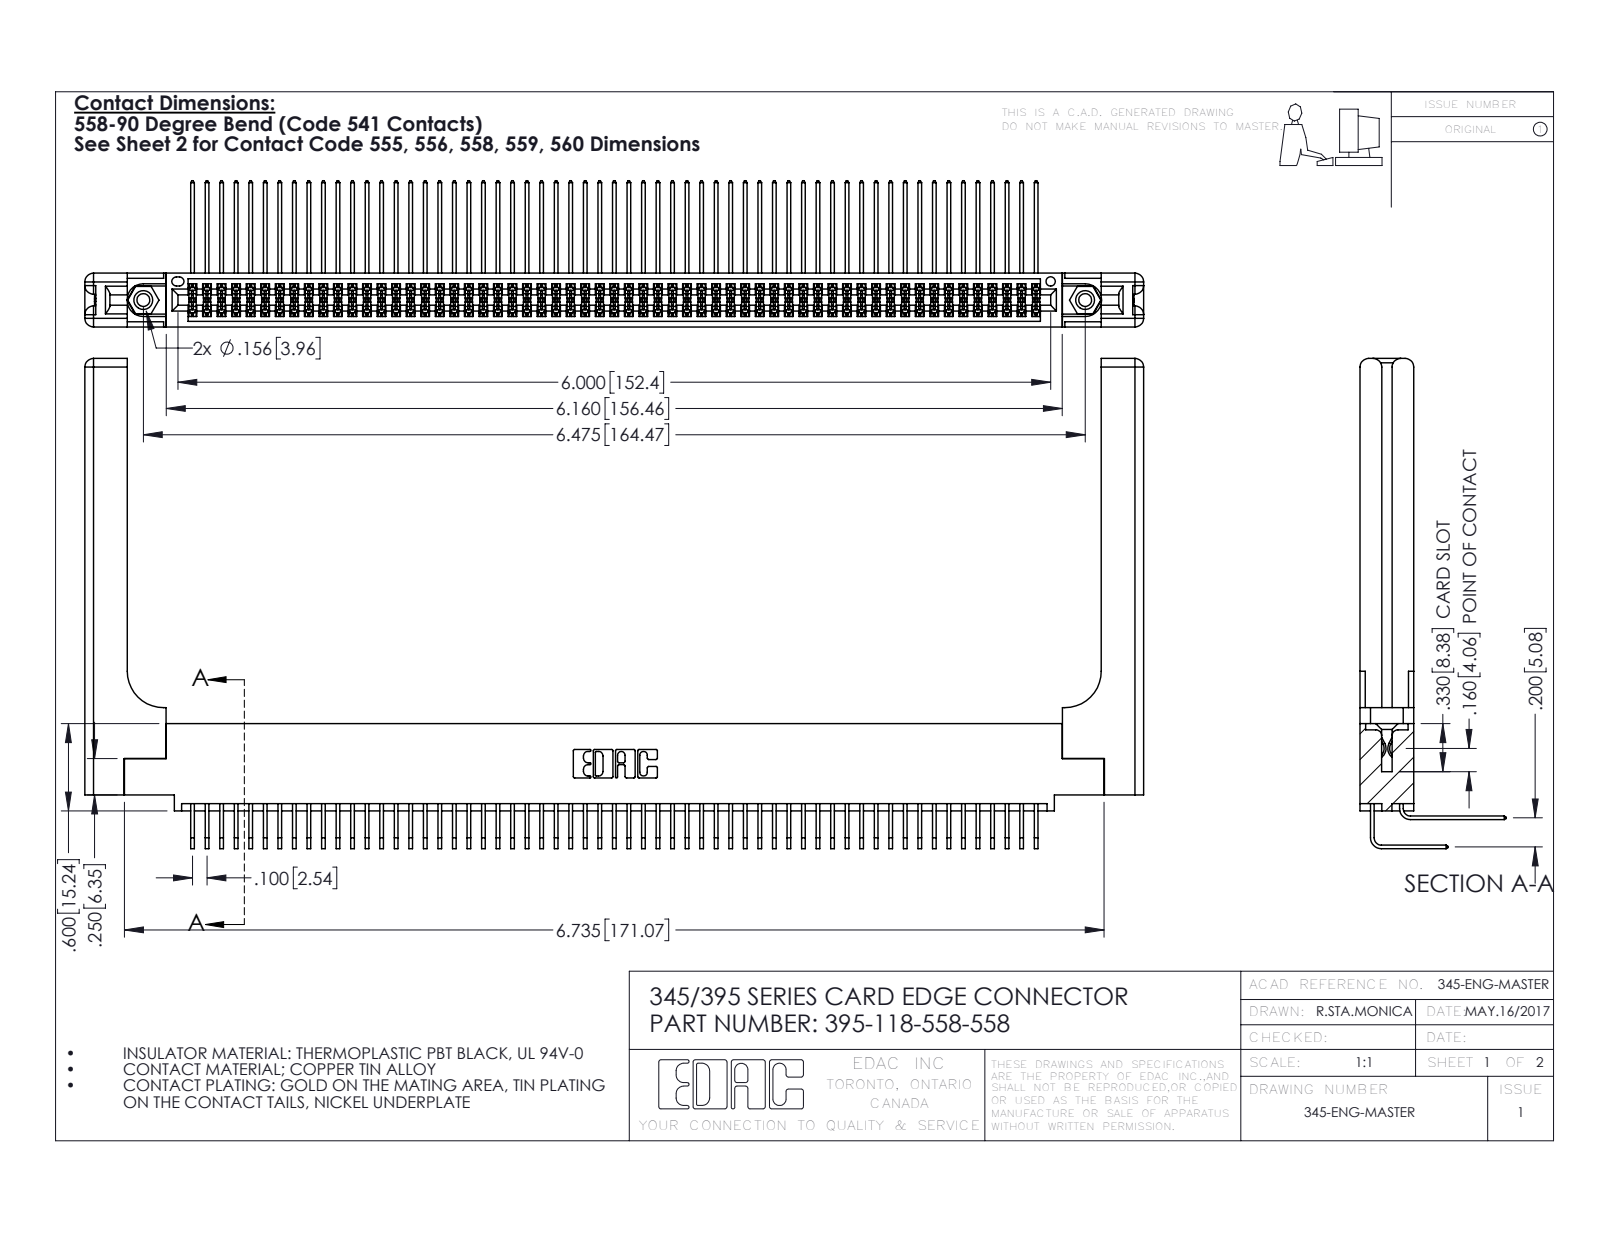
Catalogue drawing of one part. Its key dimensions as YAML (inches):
part_name: "345-220-058_345-220-058; 345 Part_0.110 Offset - 0.156 Dia-TH; 395-118-558-558; 345-292-001_558 559 Tail - 1 (+2 more)"
step_written_by: "SolidWorks 2016 (CONFIG_CONTROL_DESIGN)"
units: inches
bodies: {solids: 123, faces: 6522, planar: 4362, cylindrical: 2100, other: 60}
overall_size: [7.279, 3.369, 1.005]
volume: 1.66
surface_area: 56.36
round_holes:
  - {diameter: 0.089, count: 2}
  - {diameter: 0.125, count: 2}
  - {diameter: 0.156, count: 2}
  - {diameter: 0.064, count: 1}
round_bosses_or_shafts:
  - {diameter: 0.155, count: 2}
partial_cylinders:
  - {radius: 0.006, count: 178}
  - {radius: 0.01, count: 22}
  - {radius: 0.06, count: 16}
  - {radius: 0.007, count: 6}
  - {radius: 0.031, count: 6}
  - {radius: 0.026, count: 3}
  - {radius: 0.014, count: 2}
  - {radius: 0.019, count: 2}
face_to_face_distances: [0.072, 0.298, 0.37, 0.2, 0.098, 0.272, 0.025, 0.225, 0.148, 0.15]
hole_center_spacings: [0.27, 6.239, 6.475]
